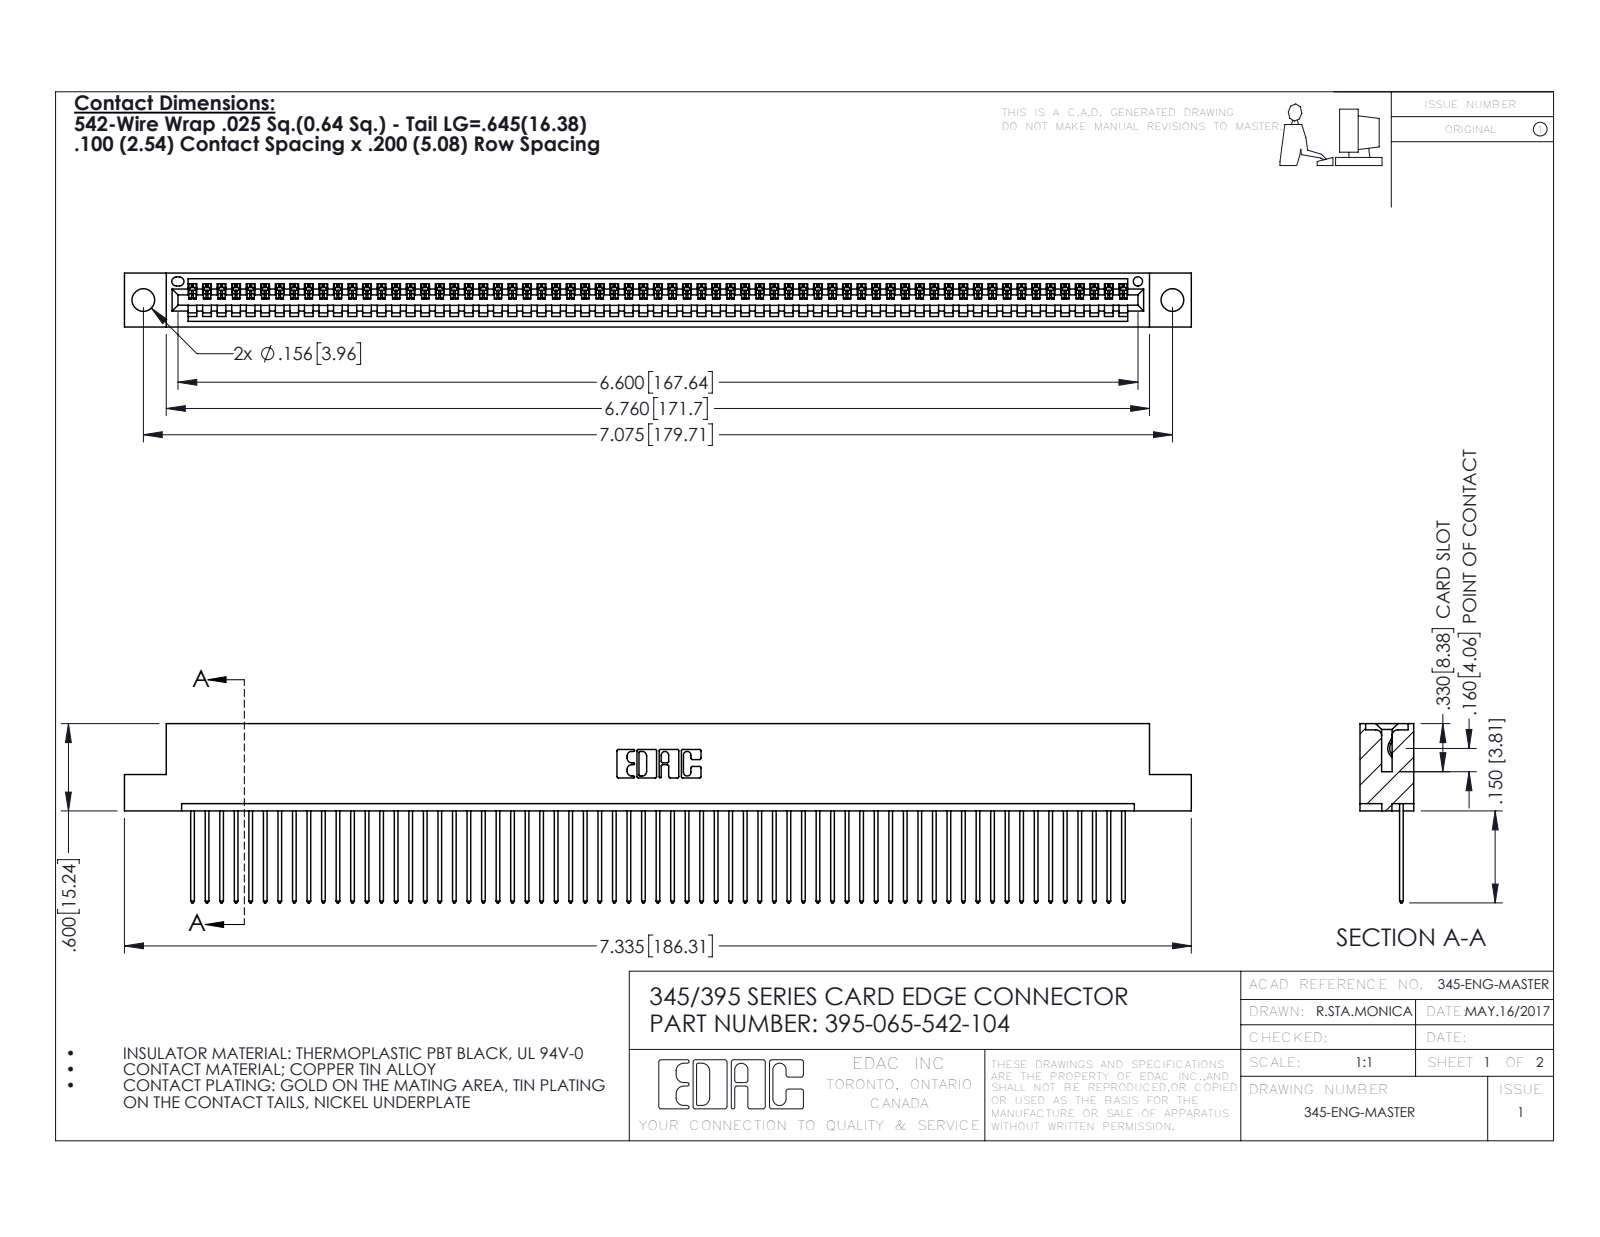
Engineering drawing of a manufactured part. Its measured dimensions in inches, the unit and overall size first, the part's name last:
Units: inches
Overall size (bounding box): 7.335 × 1.232 × 0.37
Round holes (diameter × count): ⌀0.156 ×2, ⌀0.064 ×1
Partial cylindrical surfaces — rounded edges, fillets, slot ends (radius × count): R0.006 ×130, R0.01 ×130, R0.01 ×22, R0.007 ×6, R0.031 ×6, R0.026 ×3, R0.031 ×2, R0.04 ×2
Main face-to-face distances: 0.072, 0.298, 0.098, 0.272, 0.025, 0.37, 0.2, 0.225, 0.149, 0.072
Hole centre spacings: 0.27, 6.839, 7.075
Volume: 1.095 in³ · Surface area: 38.56 in²
Bodies: 66 solids, 3896 faces (2680 planar, 1216 cylindrical, 0 other)
Part name (STEP PRODUCT): 345 Part_Flush Mounting Lugs - 0.156 Dia-TH; 345-292-001_345-293-142; 395-065-542-104
STEP written by: SolidWorks 2016 (CONFIG_CONTROL_DESIGN)
